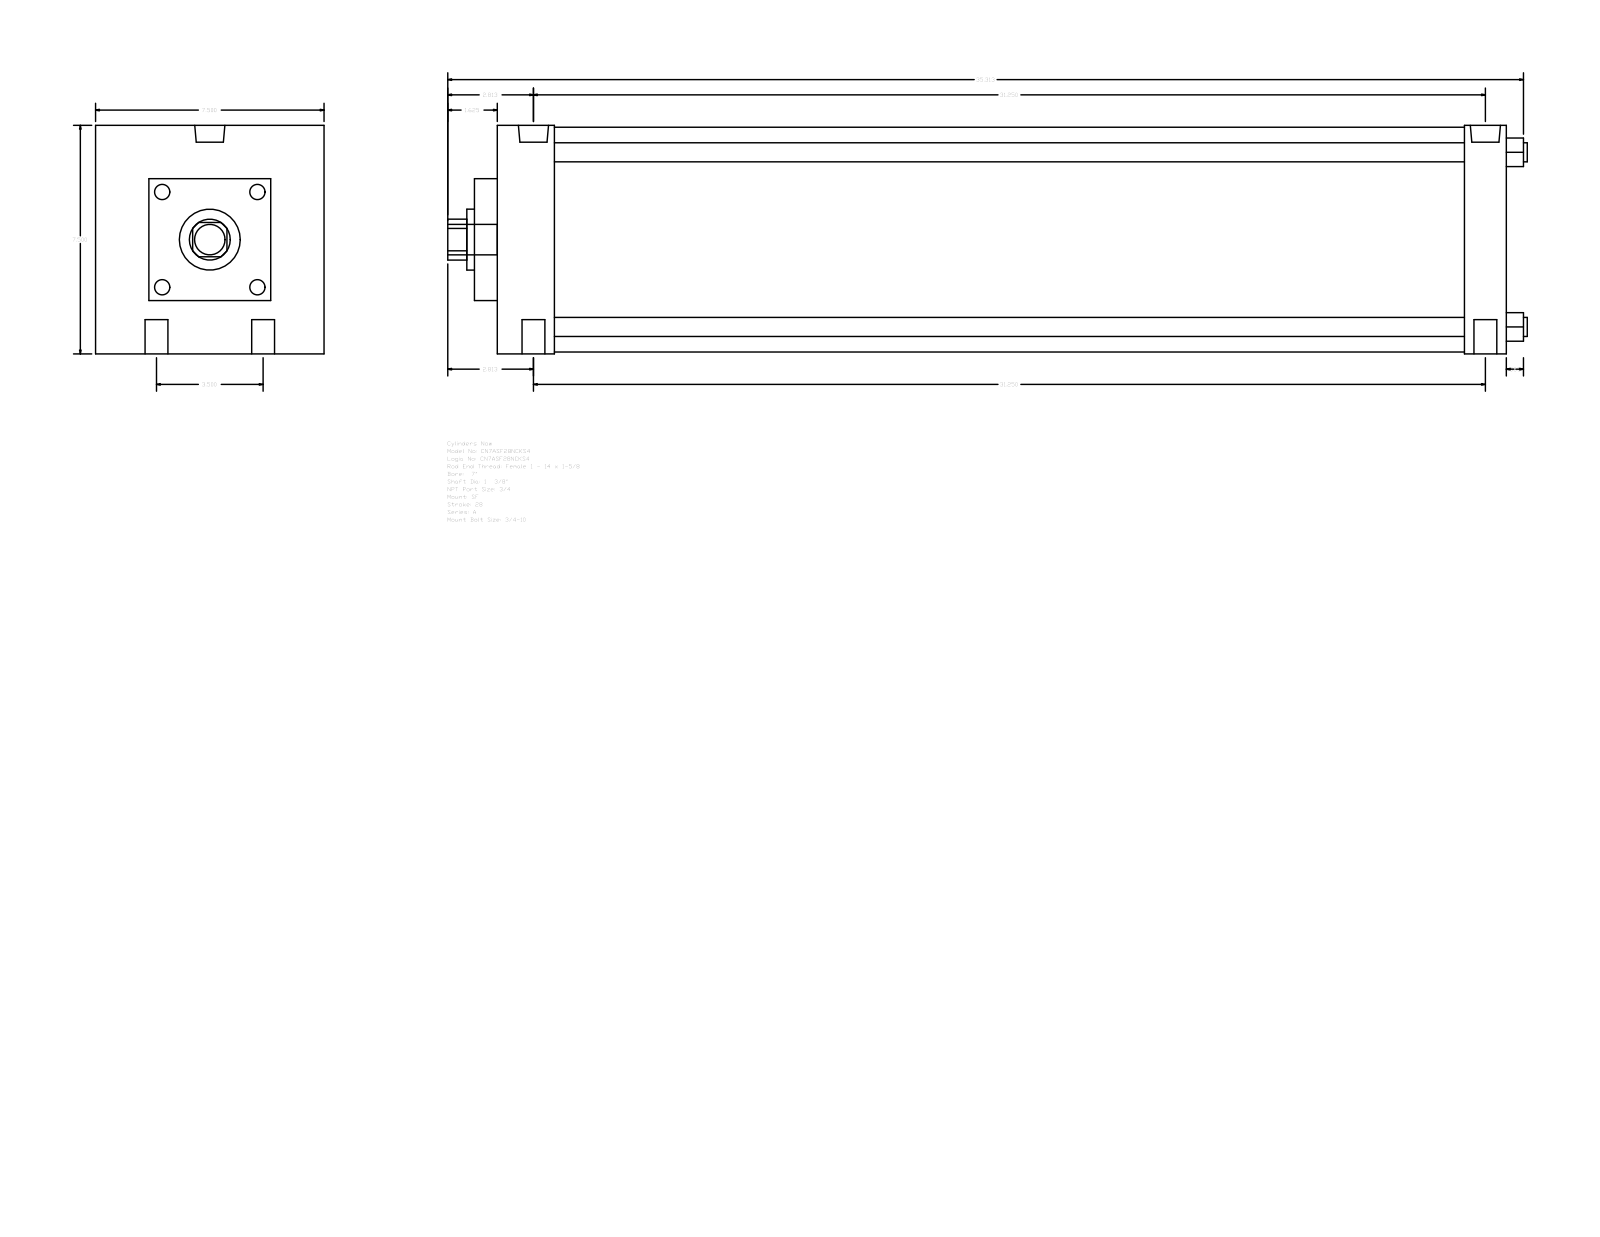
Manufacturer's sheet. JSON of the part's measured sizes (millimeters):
{"part_name": "A_SF__0700_1.375", "step_written_by": "GSSL Pune (CONFIG_CONTROL_DESIGN)", "units": "millimeters", "bodies": {"solids": 0, "faces": 93, "planar": 67, "cylindrical": 26, "other": 0}, "overall_size": [900.11, 190.5, 190.5], "round_holes": [[19.05, 4], [15.08, 2], [25.12, 2], [34.92, 1], [50.8, 1]], "round_bosses_or_shafts": [[15.88, 4], [187.32, 1], [25.4, 1]], "partial_cylinders_radius": [[17.06, 1]], "face_to_face_distances": [190.5, 841.38, 19.04, 860.42, 66.67, 825.5, 47.63, 806.46, 758.83, 793.75], "hole_center_spacings": [44.45, 794.99, 793.75, 88.9, 798.71, 782.63]}
